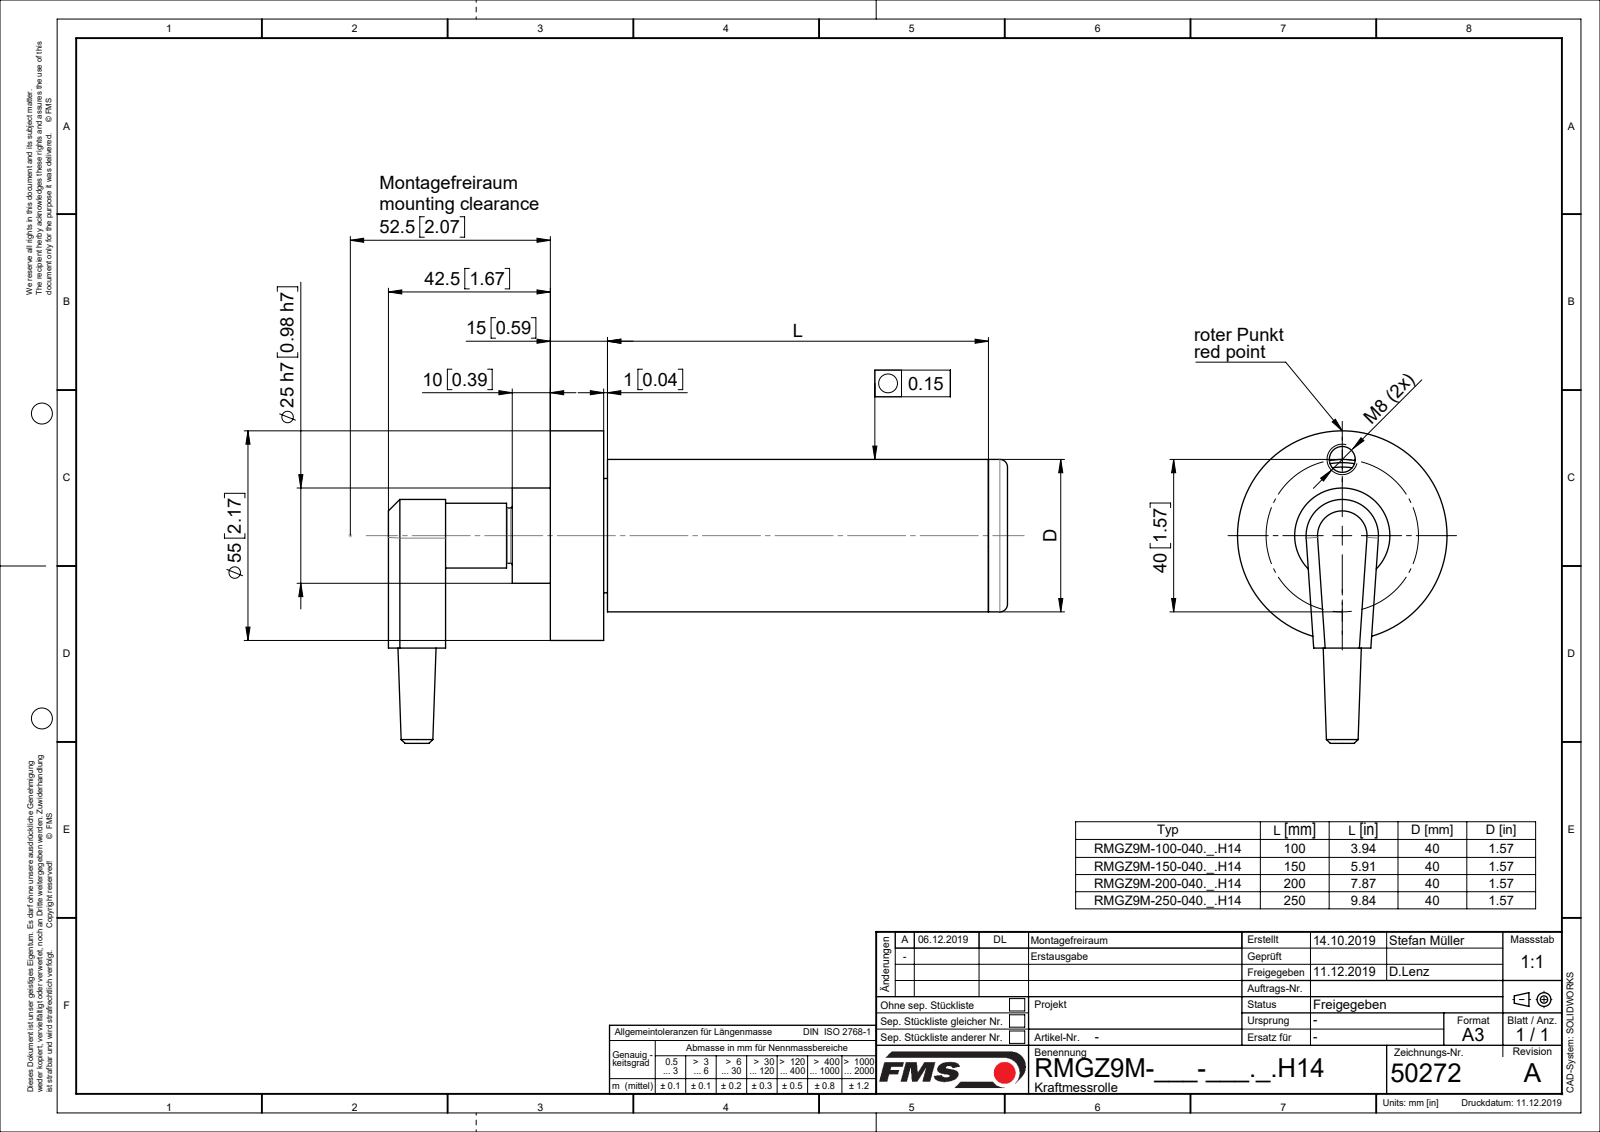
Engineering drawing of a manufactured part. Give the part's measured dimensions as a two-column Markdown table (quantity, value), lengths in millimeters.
| quantity | value |
| --- | --- |
| part name | R50272_STP; R4862004; TEIL1; RILLENKUGELLAGER_6201 (+3 more) |
| STEP written by | Mechanical Desktop 2009 (CONFIG_CONTROL_DESIGN) |
| units | millimeters |
| bodies | 6 solids, 205 faces (55 planar, 93 cylindrical, 57 other) |
| overall size | 171.49 × 82 × 55 |
| volume | 130 236 mm³ |
| surface area | 61 545 mm² |
| round holes (diameter × count) | 2 × 5, 6.91 × 2, 10 × 1, 11.5 × 1, 13.3 × 1, 26.3 × 1, 27 × 1, 28 × 1, 32 × 1, 36 × 1 |
| round bosses / shafts (diameter × count) | 55 × 1, 40 × 1, 31.3 × 1, 25 × 1, 17 × 1, 16 × 1, 14.8 × 1, 14.2 × 1 |
| partial cylindrical surfaces (radius × count) | 9.5 × 1 |
| main face-to-face distances | 14, 16, 7.4, 119.5, 14.5, 2.6, 105.5, 4.5, 117.5, 30 |
| hole center spacings | 3, 3.14, 3.65, 3.96, 6, 6.34, 6.71, 17.02 |
